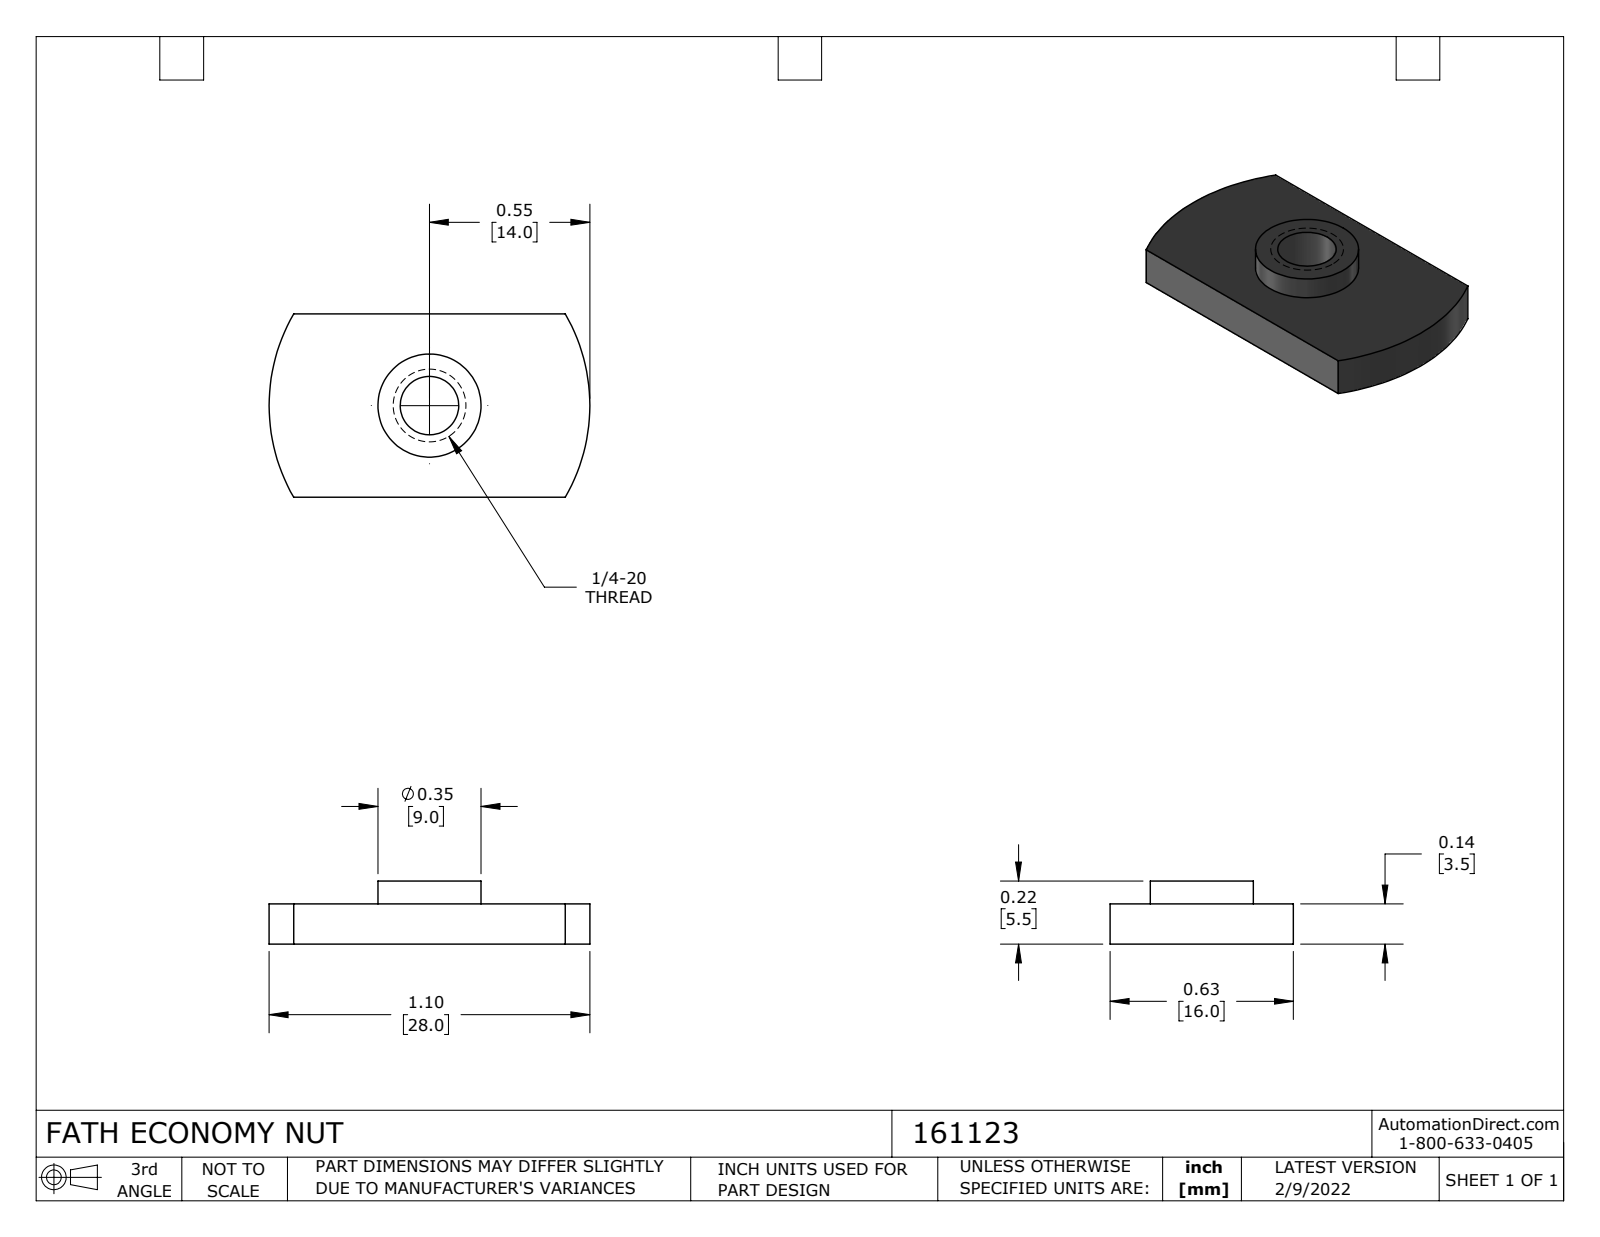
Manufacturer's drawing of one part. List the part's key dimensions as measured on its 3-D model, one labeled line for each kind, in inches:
Part name (STEP PRODUCT): 161123
STEP written by: SolidWorks 2021 (CONFIG_CONTROL_DESIGN)
Units: inches
Bodies: 1 solid, 11 faces (5 planar, 6 cylindrical, 0 other)
Overall size (bounding box): 1.102 × 0.63 × 0.217
Volume: 0.092 in³ · Surface area: 1.92 in²
Round holes (diameter × count): ⌀0.201 ×1
Round bosses / shafts (diameter × count): ⌀0.354 ×1
Partial cylindrical surfaces — rounded edges, fillets, slot ends (radius × count): R0.63 ×2
Main face-to-face distances: 0.138, 0.63, 0.217, 0.079
